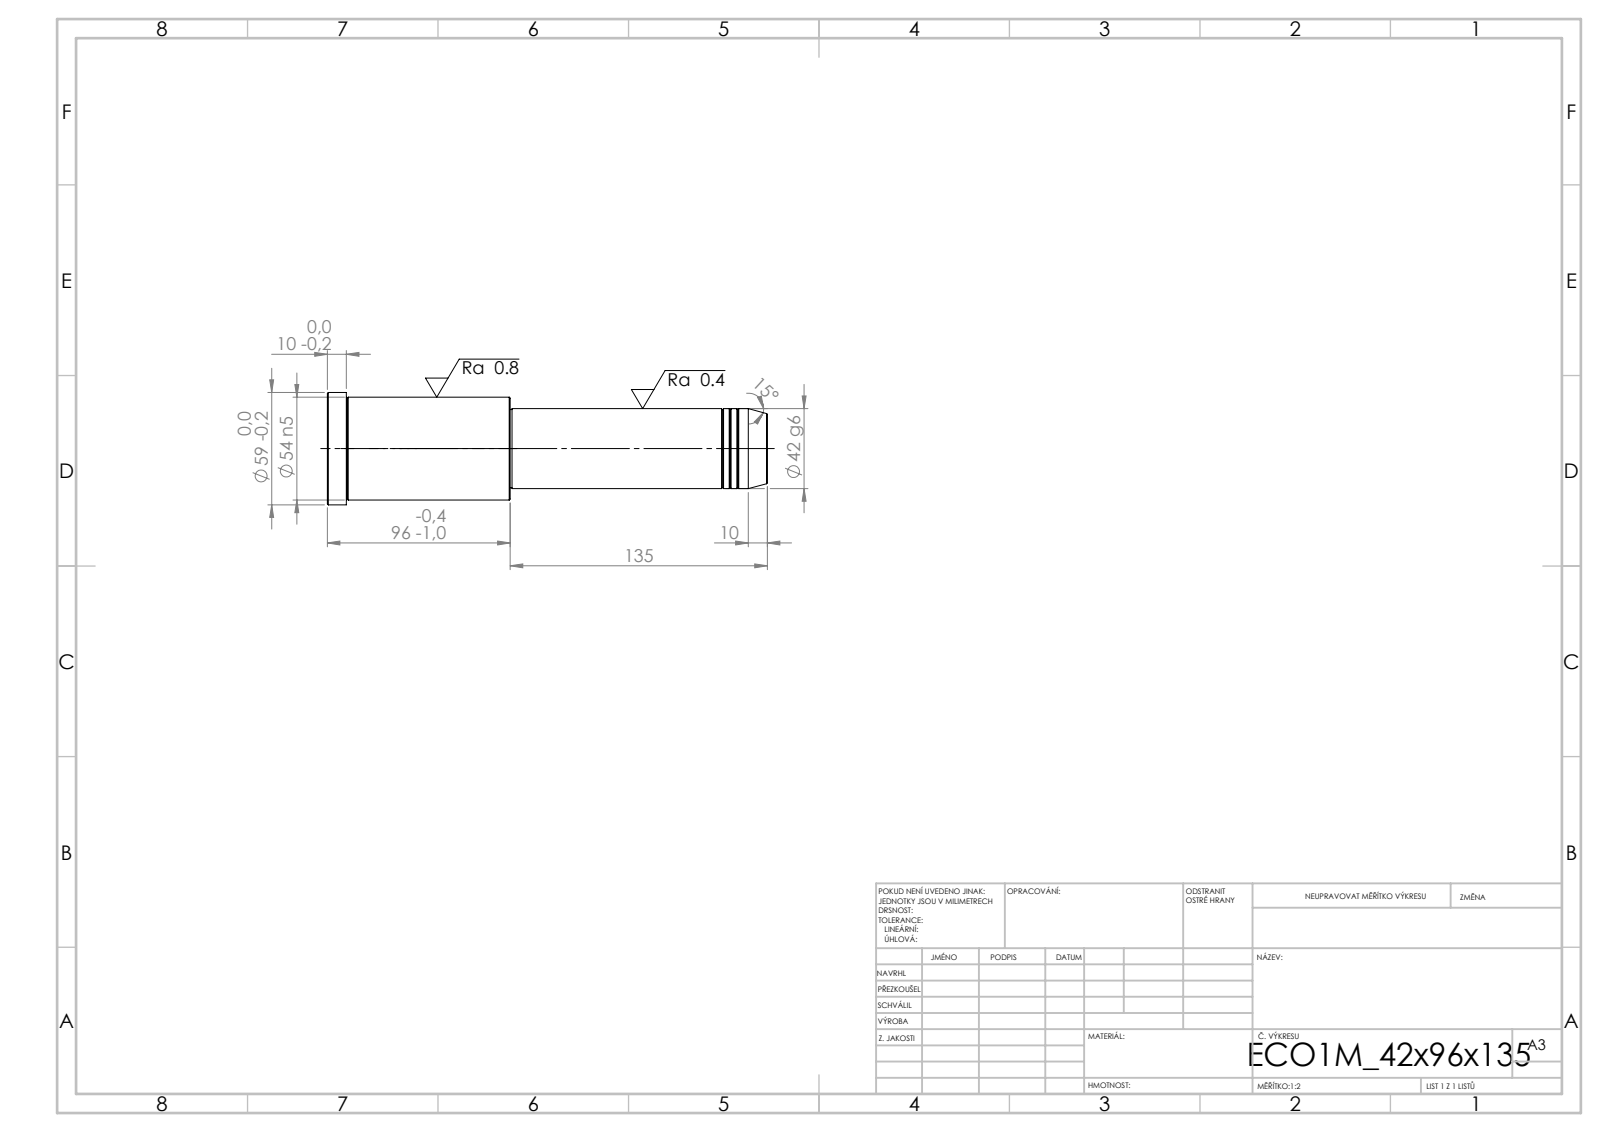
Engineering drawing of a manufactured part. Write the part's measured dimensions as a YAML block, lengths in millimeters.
step_written_by: "SolidWorks 2019 (CONFIG_CONTROL_DESIGN)"
units: millimeters
bodies: {solids: 1, faces: 43, planar: 5, cylindrical: 14, other: 24}
overall_size: [231, 59, 59]
volume: 409308
surface_area: 39672
round_bosses_or_shafts:
  - {diameter: 59, count: 1}
  - {diameter: 54, count: 1}
  - {diameter: 42, count: 1}
  - {diameter: 41, count: 1}
face_to_face_distances: [231, 135, 96, 221, 86, 10, 134, 1, 87, 97]
